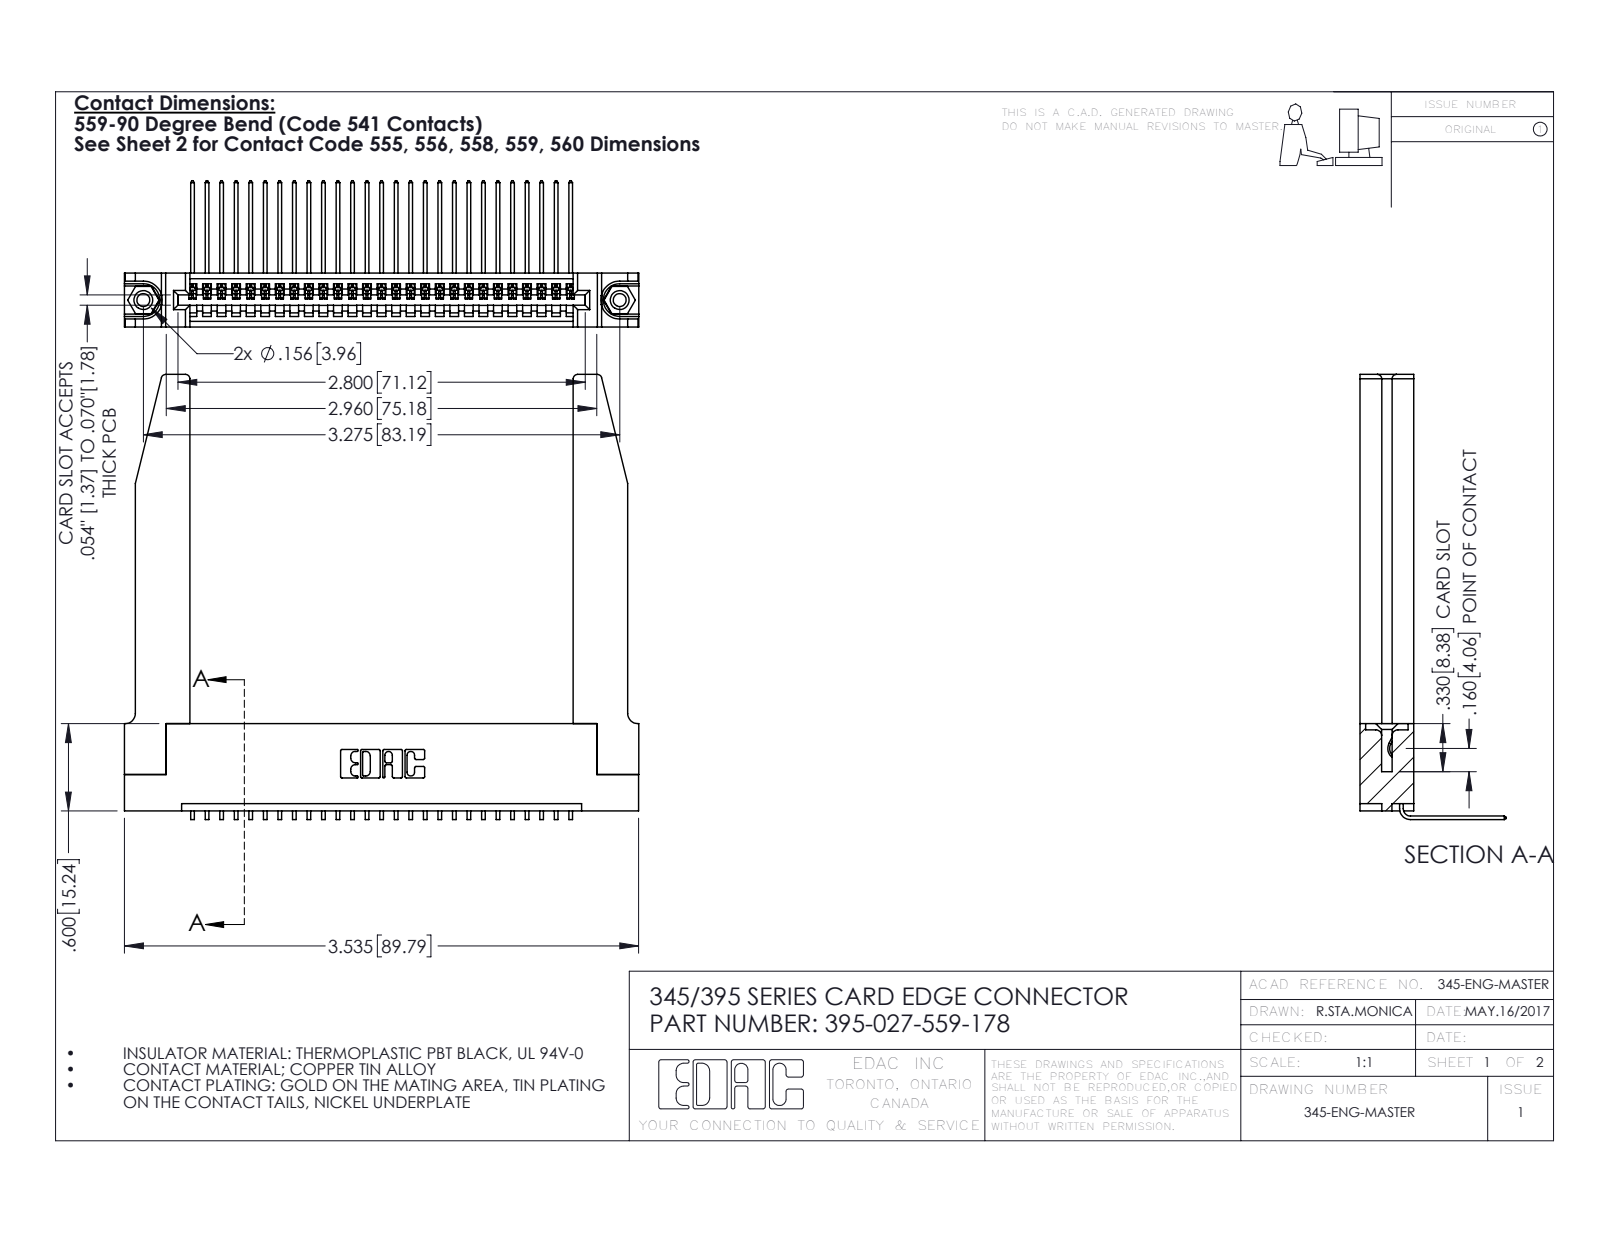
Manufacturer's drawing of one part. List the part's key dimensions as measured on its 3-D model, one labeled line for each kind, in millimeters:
Part name (STEP PRODUCT): 345-292-001_558 559 Tail - 1; 345-250-001_345-250-001-102; 345 Part_Flush Mounting Lugs - 0.156 Dia-TH; 345-220-078_345-220-078 (+1 more)
STEP written by: SolidWorks 2016 (CONFIG_CONTROL_DESIGN)
Units: millimetres
Bodies: 32 solids, 1980 faces (1356 planar, 572 cylindrical, 52 other)
Overall size (bounding box): 89.8 × 77.7 × 25.5
Volume: 16 300 mm³ · Surface area: 18 460 mm²
Round holes (diameter × count): ⌀2.3 ×2, ⌀3.2 ×2, ⌀4 ×2, ⌀1.6 ×1
Round bosses / shafts (diameter × count): ⌀3.9 ×2
Partial cylindrical surfaces — rounded edges, fillets, slot ends (radius × count): R0.2 ×54, R0.3 ×22, R0.8 ×8, R0.2 ×6, R0.8 ×6, R0.7 ×3, R0.8 ×2, R1 ×2
Main face-to-face distances: 9.4, 1.8, 7.6, 5.1, 2.5, 6.9, 0.6, 3.8, 3.8, 5.7
Hole centre spacings: 6.9, 77.2, 83.2
